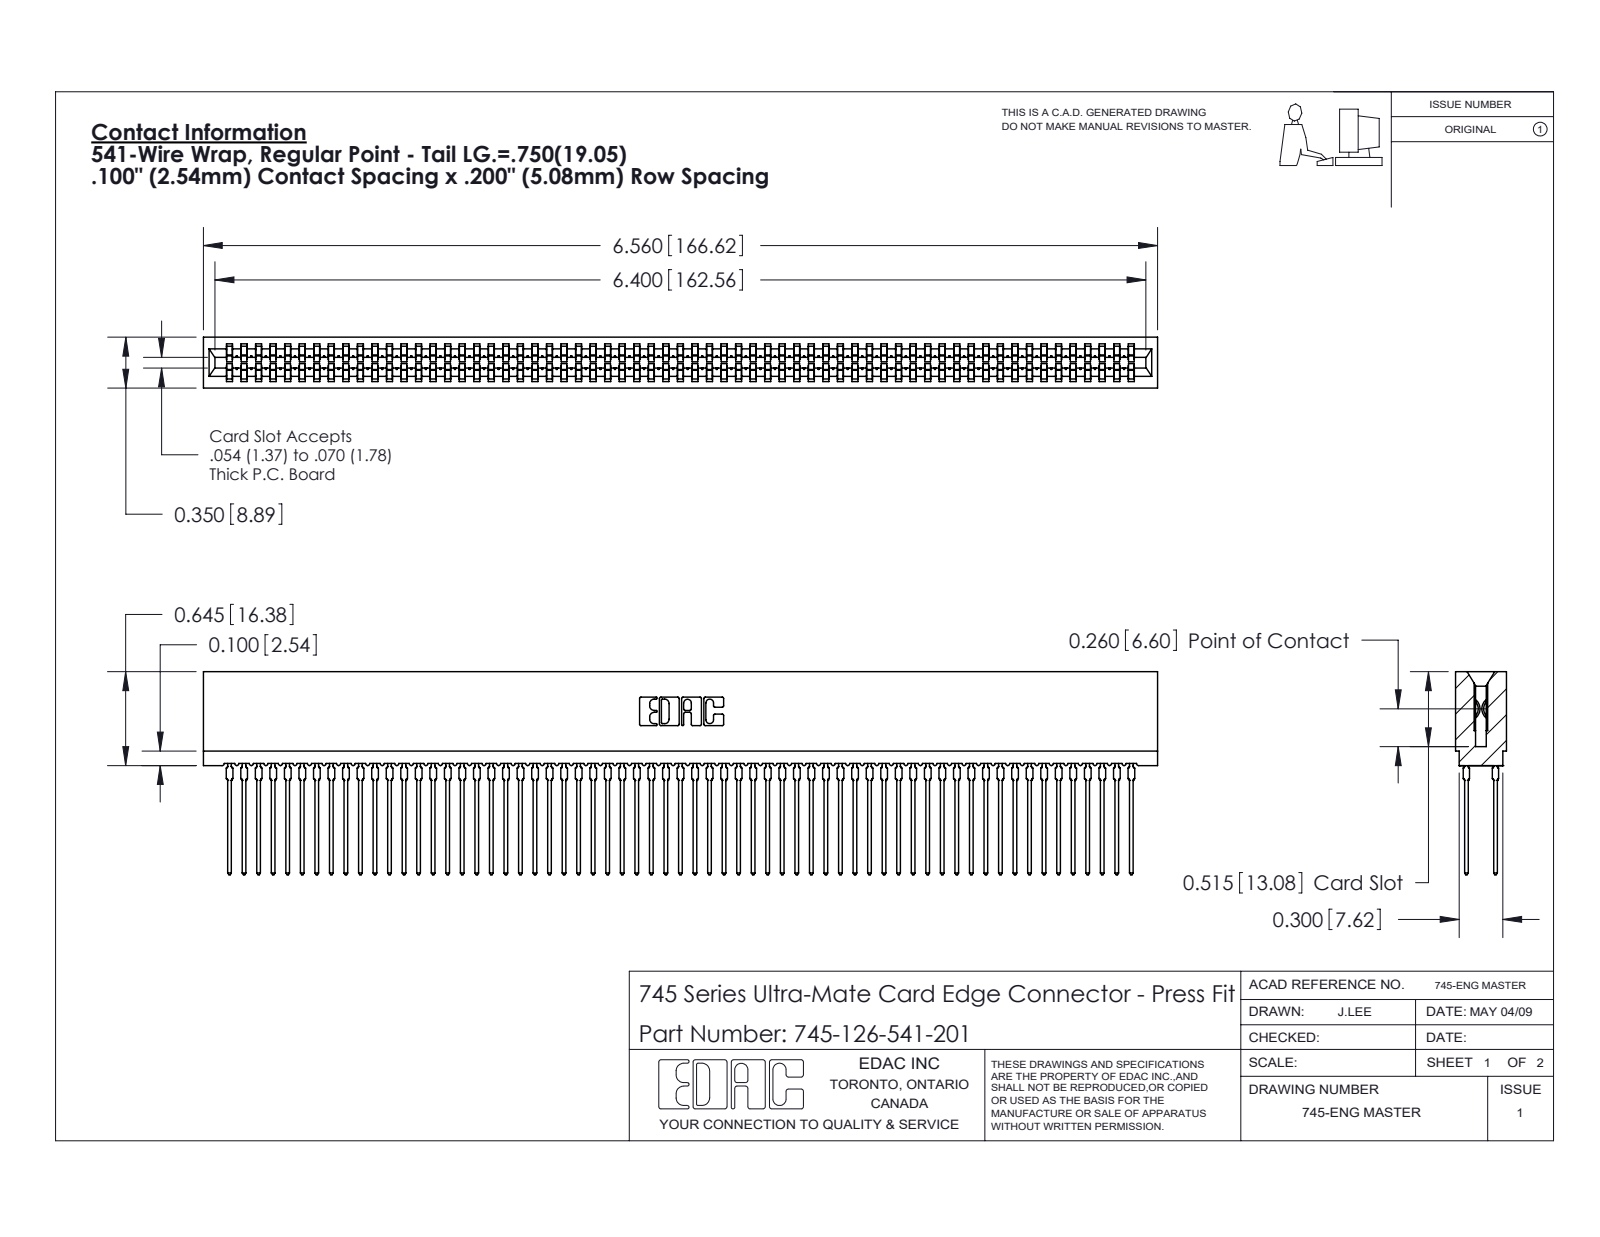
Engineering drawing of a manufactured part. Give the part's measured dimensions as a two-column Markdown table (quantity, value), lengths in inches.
| quantity | value |
| --- | --- |
| part name | 745 Part_Insulator Option - 01; 745-126-541-201; 745-292-001_541 |
| STEP written by | SolidWorks 2020 (CONFIG_CONTROL_DESIGN) |
| units | inches |
| bodies | 127 solids, 11372 faces (5851 planar, 2245 cylindrical, 3276 other) |
| overall size | 6.56 × 1.396 × 0.35 |
| volume | 0.946 in³ |
| surface area | 53.46 in² |
| partial cylindrical surfaces (radius × count) | 0.021 × 252, 0.015 × 126, 0.01 × 22, 0.005 × 8, 0.011 × 8, 0.007 × 6, 0.031 × 6, 0.026 × 3 |
| main face-to-face distances | 0.063, 0.287, 0.2, 0.35, 0.087, 0.263, 0.025, 0.045, 0.305, 0.018 |
